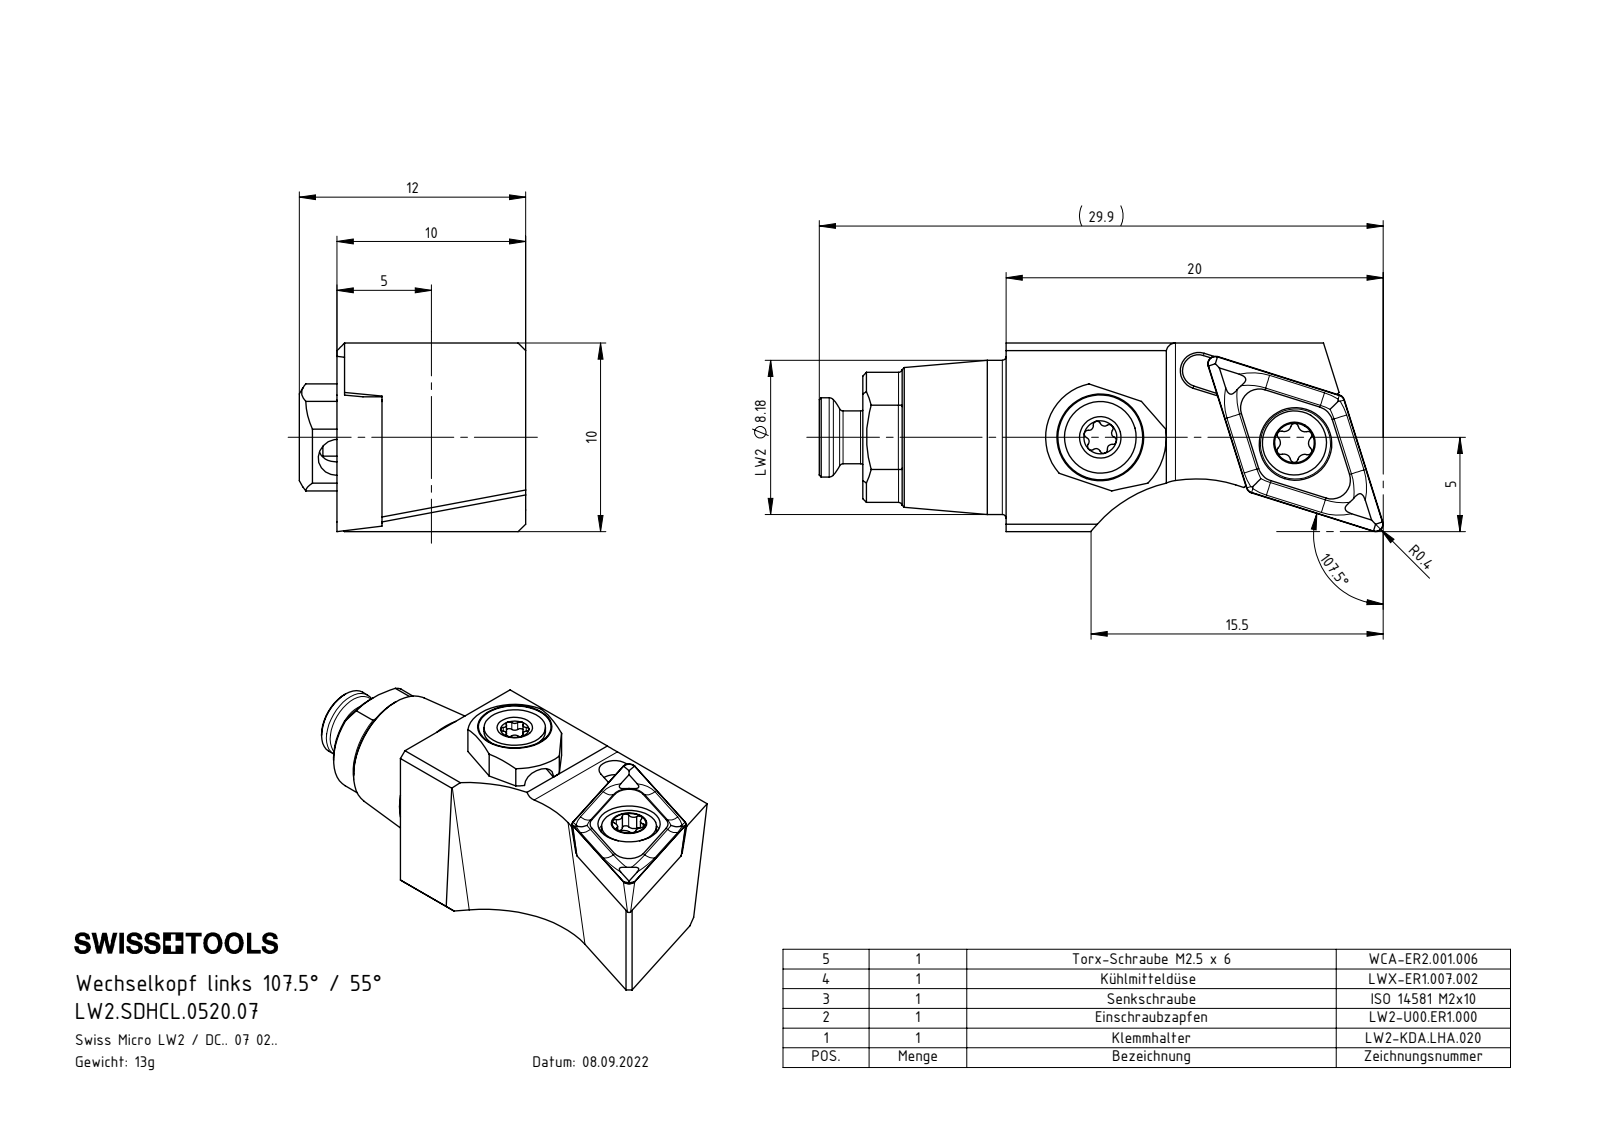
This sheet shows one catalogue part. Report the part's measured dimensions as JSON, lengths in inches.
{"part_name": "LW2.SDHCL.0520.07; ISO 14581 - M2x10; LW2-U00.ER1.000_A; LWX-ER1.007.002 (+3 more)", "step_written_by": "SolidWorks 2022 (CONFIG_CONTROL_DESIGN)", "units": "inches", "bodies": {"solids": 6, "faces": 259, "planar": 66, "cylindrical": 93, "other": 100}, "overall_size": [1.177, 0.472, 0.394], "volume_in3": 0.108, "surface_area_in2": 2.714, "round_holes": [[0.039, 1], [0.059, 1], [0.063, 1], [0.081, 1], [0.11, 1], [0.118, 1], [0.138, 1], [0.152, 1]], "round_bosses_or_shafts": [[0.322, 1], [0.165, 1], [0.157, 1], [0.15, 1], [0.134, 1], [0.118, 1], [0.11, 1], [0.098, 1]], "partial_cylinders_radius": [[0.008, 8], [0.007, 6], [0.008, 6], [0.009, 6], [0.011, 6], [0.014, 5], [0.014, 1], [0.02, 1]], "face_to_face_distances": [0.394, 0.3, 0.094, 0.378, 0.078, 0.016, 0.299, 0.079, 0.043, 0.315], "hole_center_spacings": [0.406, 0.408]}
